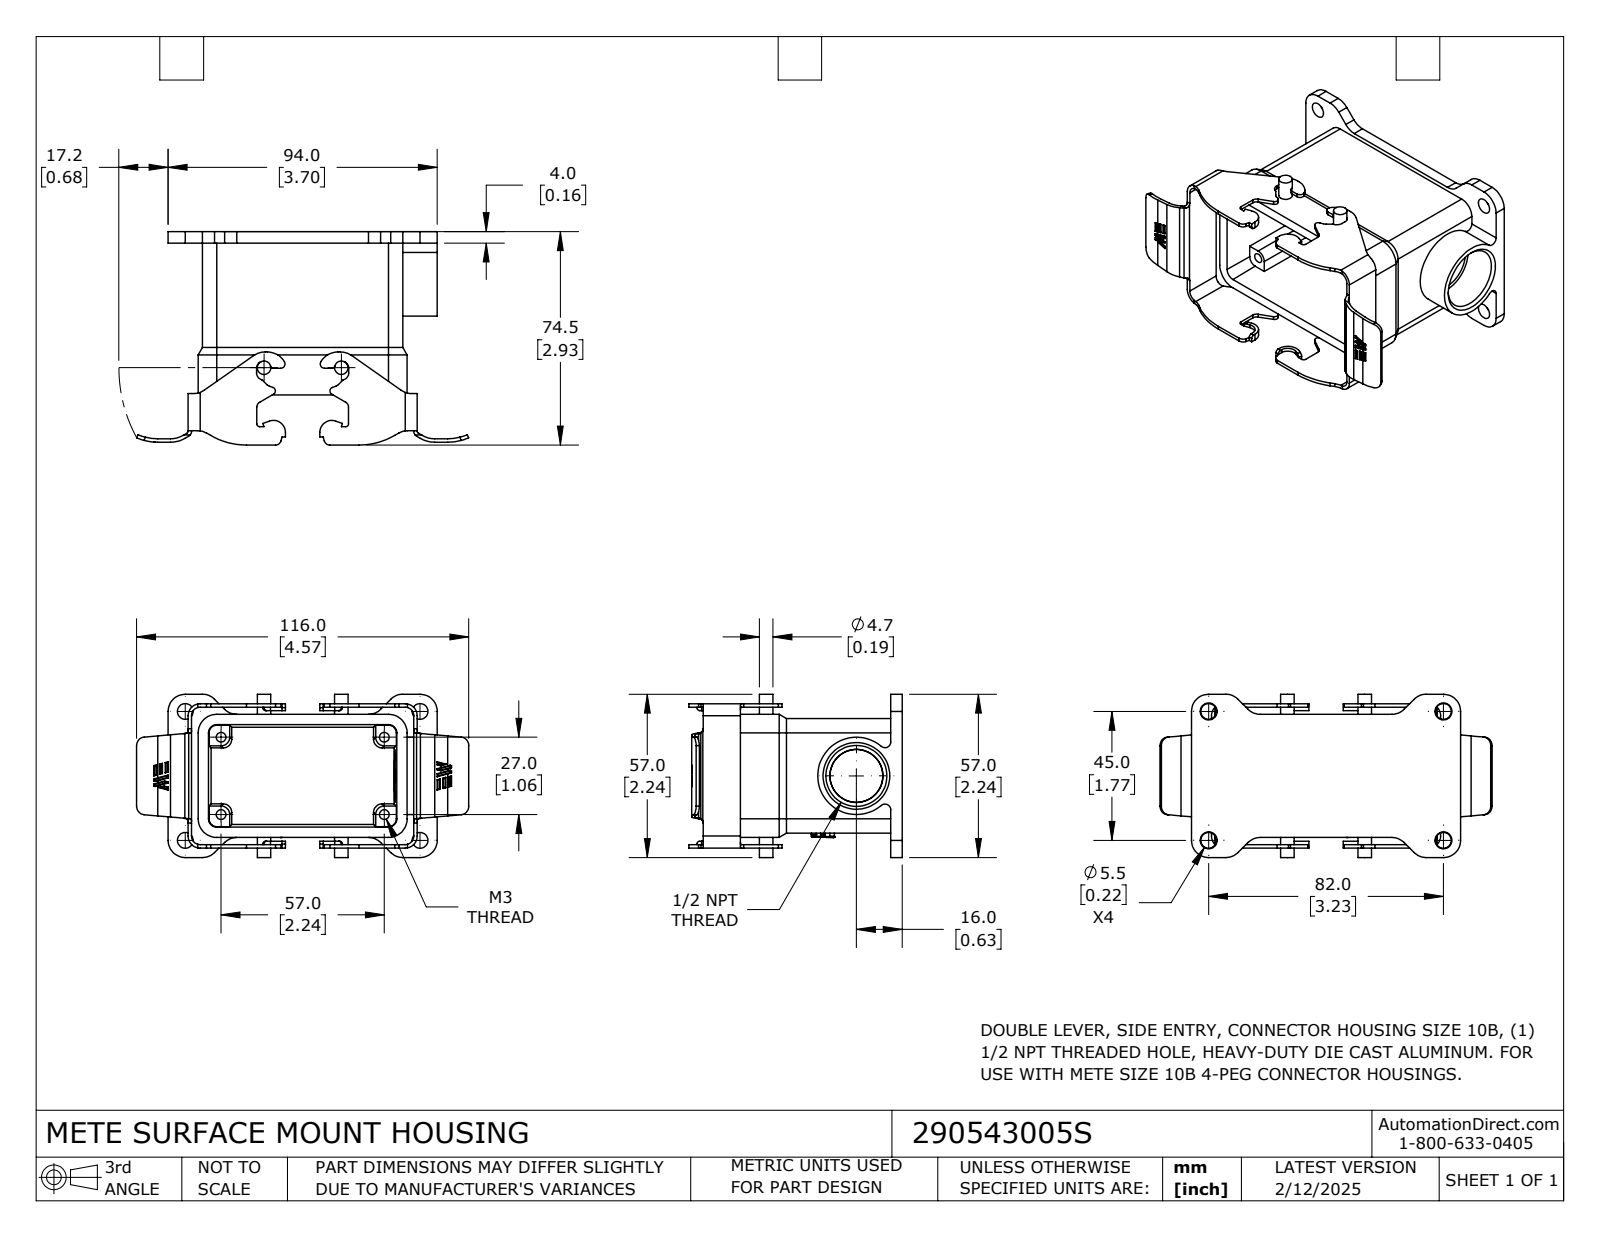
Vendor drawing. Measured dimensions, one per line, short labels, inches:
name: 290543005S
written by: SolidWorks 2024 (CONFIG_CONTROL_DESIGN)
unit: in
bodies: 1 solid, 477 faces (210 planar, 239 cylindrical, 28 other)
size: 4.567 × 2.933 × 2.244
volume: 4.064 in³; area: 69.39 in²
holes: 4× ⌀0.134, 1× ⌀0.839
bosses: 2× ⌀0.185
rounds: 58× R0.008, 16× R0.236, 14× R0.118, 10× R0.039, 8× R0.079, 6× R0.059, 6× R0.098, 6× R0.165
face distances: 0.157, 0.047, 0.059, 0.205, 1.78, 1.937, 1.732, 1.575, 0.146, 1.839
hole spacings: 1.063, 2.244, 2.483
